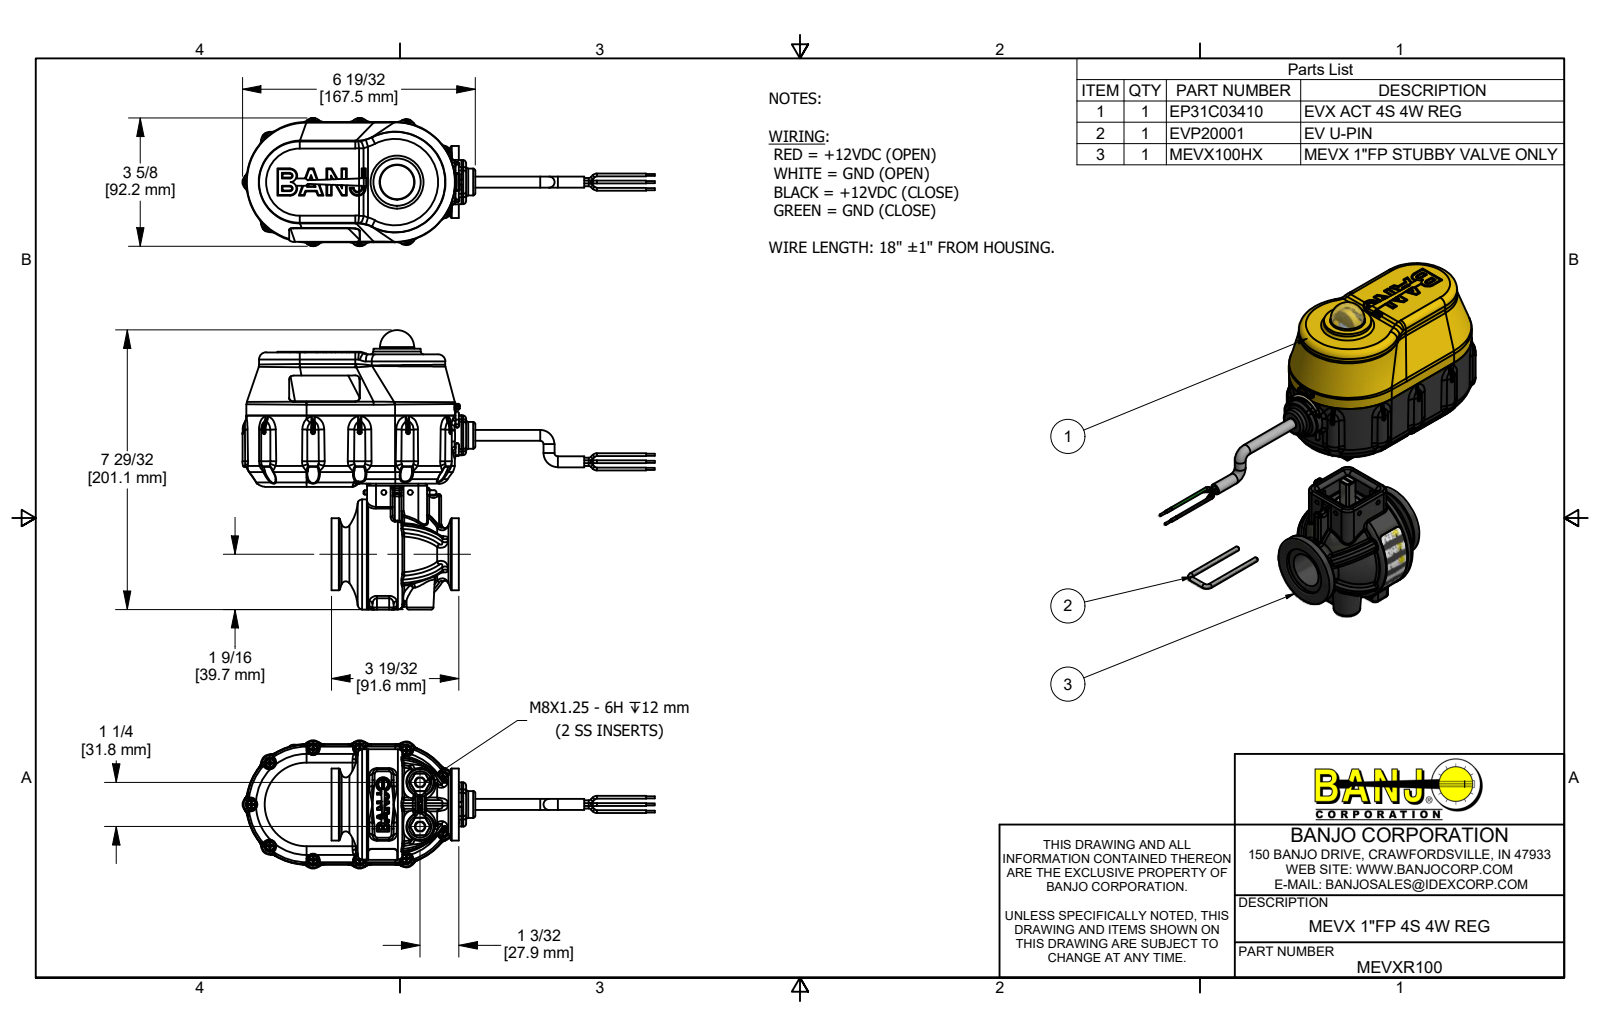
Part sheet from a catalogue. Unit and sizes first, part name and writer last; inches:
Units: inches
Overall size (bounding box): 11.685 × 7.916 × 3.63
Round holes (diameter × count): ⌀0.15 ×13, ⌀0.095 ×11, ⌀0.135 ×5, ⌀0.107 ×4, ⌀0.126 ×4, ⌀0.136 ×4, ⌀0.17 ×4, ⌀0.089 ×2, ⌀0.105 ×2, ⌀0.115 ×2, ⌀0.118 ×2, ⌀0.123 ×2
Round bosses / shafts (diameter × count): ⌀0.08 ×20, ⌀0.25 ×17, ⌀0.14 ×11, ⌀0.108 ×11, ⌀0.085 ×11, ⌀0.058 ×8, ⌀0.27 ×4, ⌀0.219 ×4
Partial cylindrical surfaces — rounded edges, fillets, slot ends (radius × count): R0.04 ×147, R0.02 ×83, R0.01 ×56, R0.06 ×50, R0.005 ×43, R0.08 ×28, R0.03 ×26, R0.125 ×26
Main face-to-face distances: 0.1, 2.565, 1.685, 0.78, 2.465, 0.88, 0.035, 0.987, 3.005, 0.055
Hole centre spacings: 1.79, 1.283, 1.662, 2.73, 2.967, 3.45, 0.487, 0.492
Volume: 46.42 in³ · Surface area: 523 in²
Bodies: 83 solids, 12238 faces (3696 planar, 3074 cylindrical, 5468 other)
Part name (STEP PRODUCT): MEVXR100; EP31C03410; 91400A119; 95584A200 (+8 more)
STEP written by: Autodesk Inventor 2019 (AUTOMOTIVE_DESIGN)
